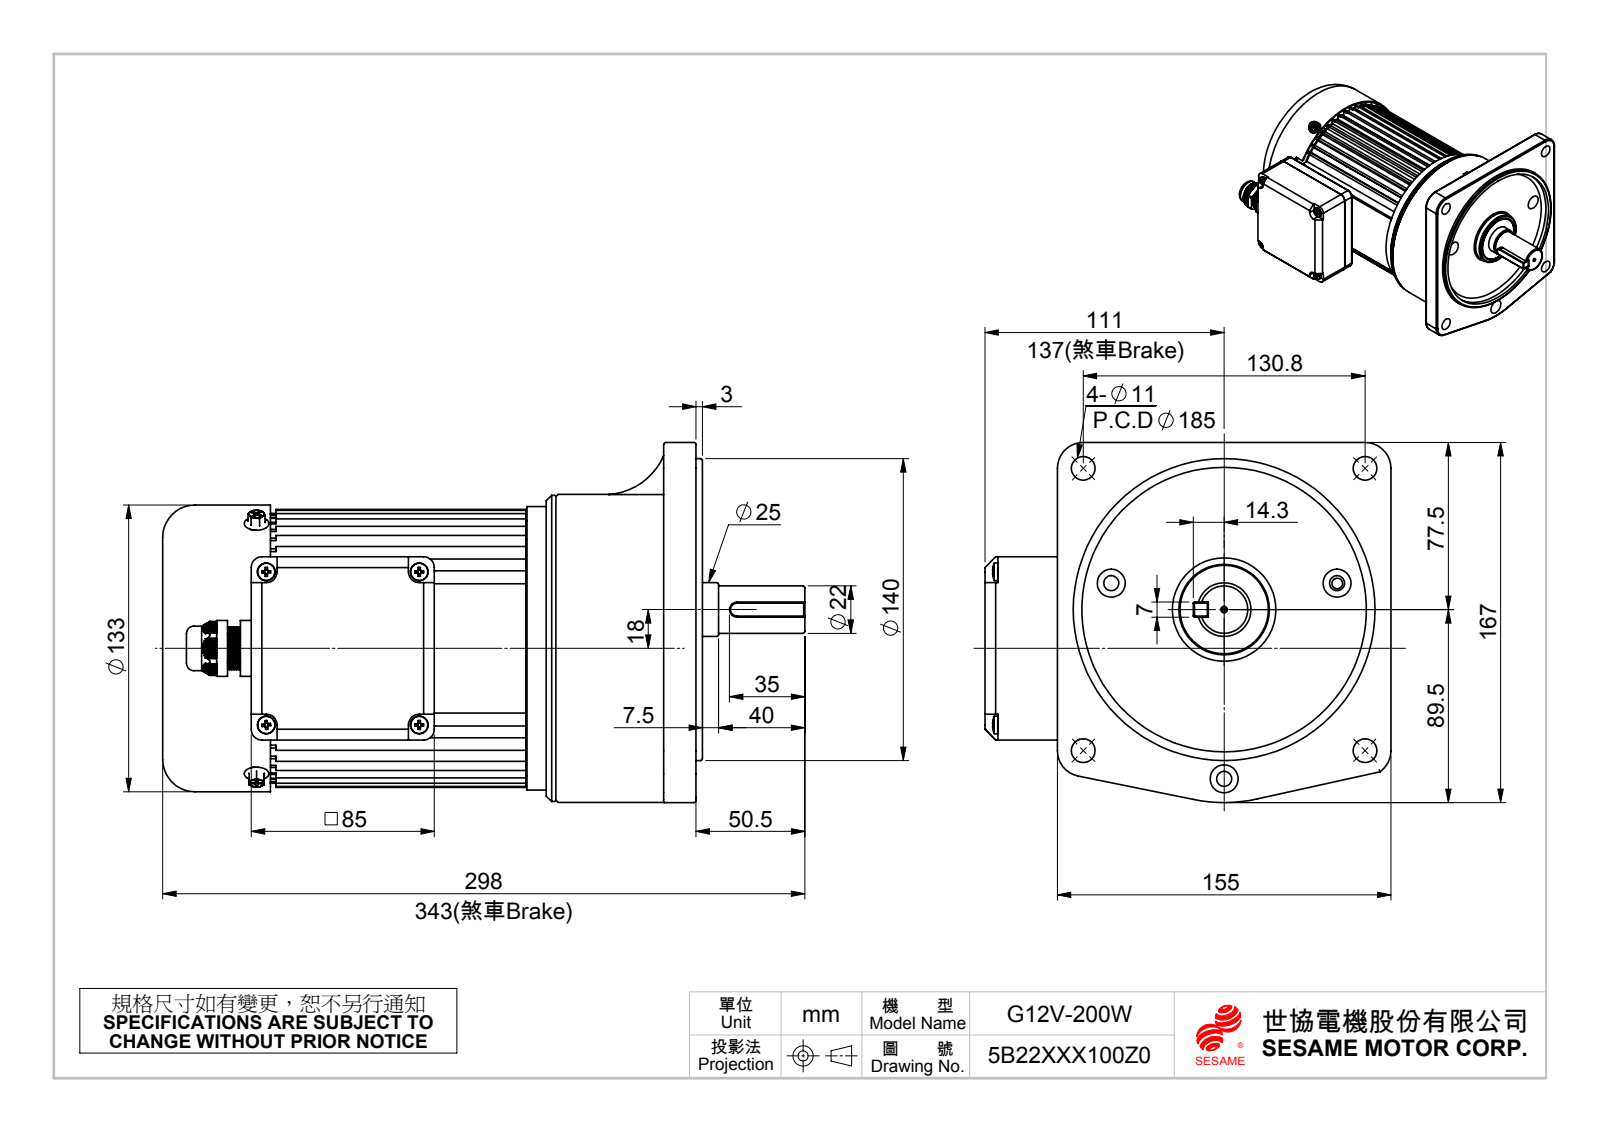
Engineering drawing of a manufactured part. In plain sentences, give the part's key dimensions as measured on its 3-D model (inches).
The part is named "油封42x25x8; 100W風扇蓋131x50／缺口70(直角); 7x7xL_35L; (標準品)G12V200W(5B22XXX100)(減速比共用) (+8 more)". Its 3-D file was written by "SolidWorks 2010 (CONFIG_CONTROL_DESIGN)". It is 19 solids with 2749 faces: 818 planar, 884 cylindrical and 1047 other. Overall it measures 11.732 by 7.417 by 6.575 inches. Its volume is 201 cubic inches and its surface area 714.7 square inches. Round holes: 14 of diameter 0.197, 9 of diameter 0.13, 7 of diameter 0.433, 4 of diameter 0.315, 3 of diameter 0.165, 3 of diameter 0.276, 3 of diameter 0.512, 1 of diameter 0.079, 1 of diameter 0.295, 1 of diameter 0.425, 1 of diameter 0.65, 1 of diameter 0.982. Round bosses or shafts: 4 of diameter 0.327, 4 of diameter 0.157, 3 of diameter 0.197, 1 of diameter 5.622, 1 of diameter 5.591, 1 of diameter 5.512, 1 of diameter 5.236, 1 of diameter 5.177. Partial cylindrical surfaces (rounded edges, fillets, slot ends): 101 of radius 0.039, 8 of radius 0.041, 8 of radius 0.079, 8 of radius 0.197, 6 of radius 0.108, 4 of radius 0.1, 4 of radius 0.14, 3 of radius 0.472. The main face-to-face distances are 0.079, 0.394, 2.362, 5.47, 0.118, 0.709, 5.864, 4.331, 0.138, 7.833. The hole center spacings are 2.382, 4.126, 1.772, 2.795, 1.226, 0.433, 0.453, 0.575.
